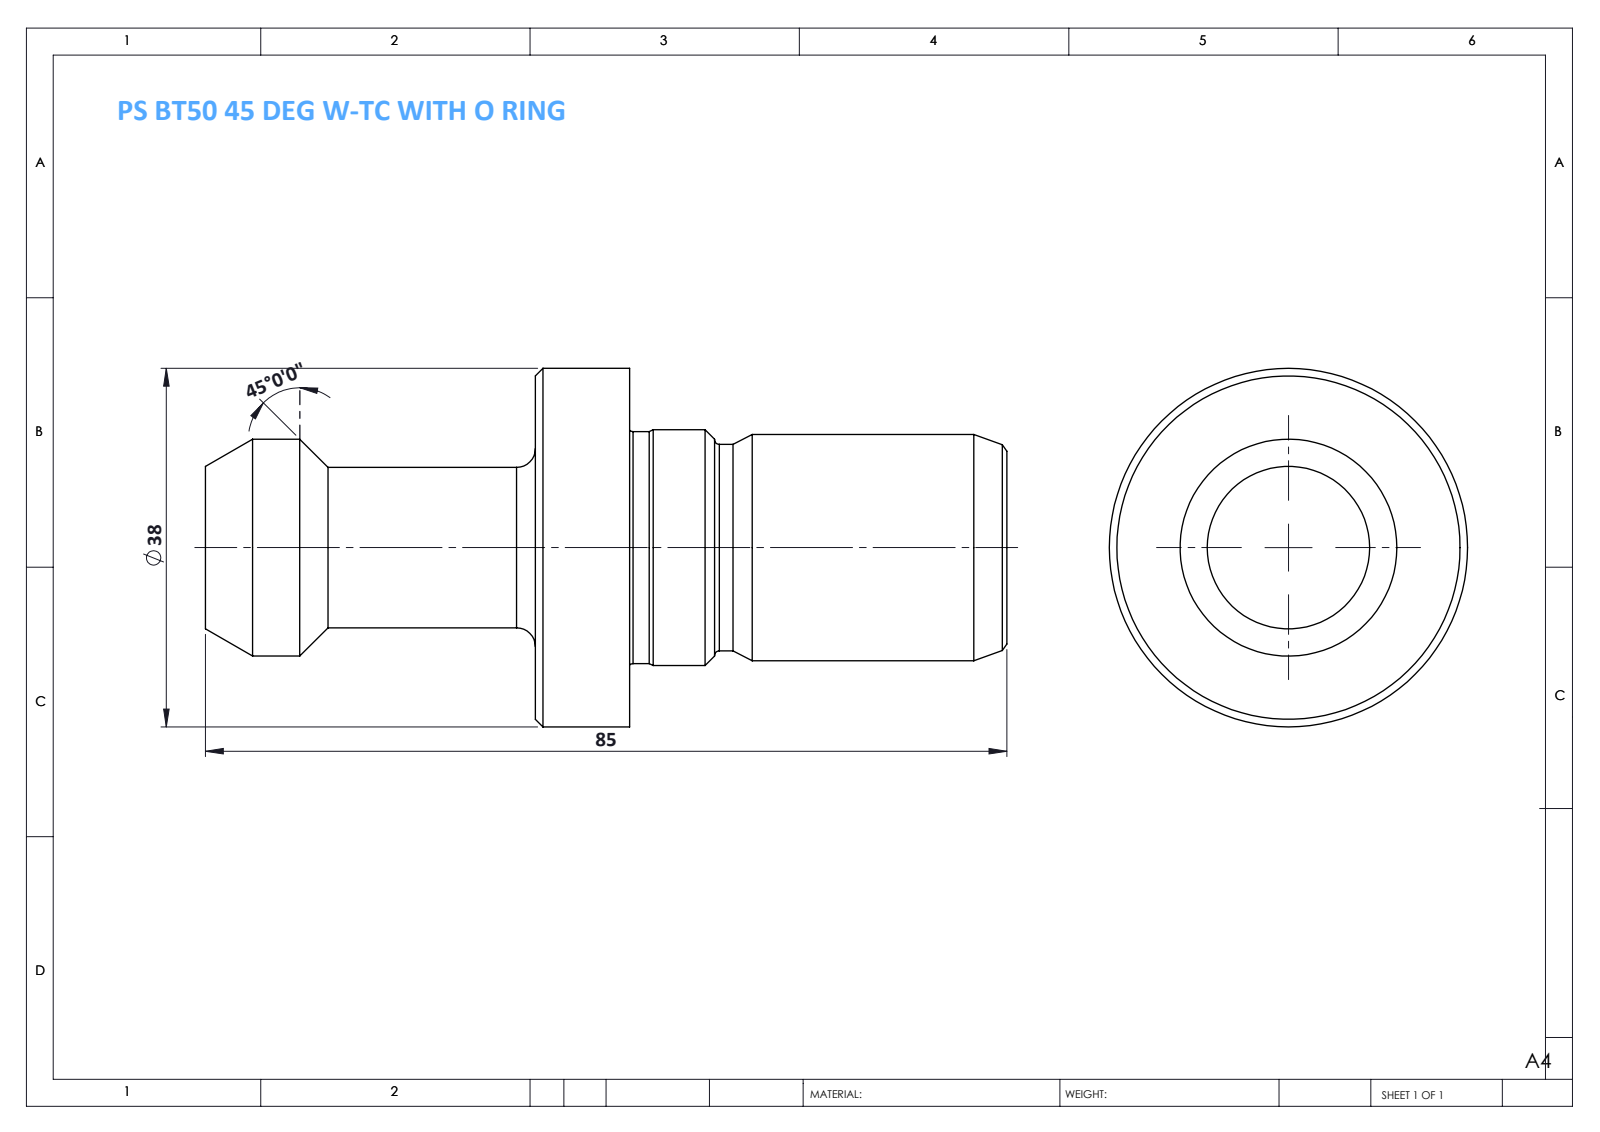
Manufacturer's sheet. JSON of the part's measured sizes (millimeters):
{"part_name": "PS BT50 45 DEG W-TC WITH O RING", "step_written_by": "SolidWorks 2014 (CONFIG_CONTROL_DESIGN)", "units": "millimeters", "bodies": {"solids": 1, "faces": 43, "planar": 5, "cylindrical": 14, "other": 24}, "overall_size": [85, 38, 38], "volume_mm3": 38941, "surface_area_mm2": 8503, "round_bosses_or_shafts": [[38, 1], [25, 1], [24.6, 1], [24, 1], [23, 1], [21.9, 1], [17, 1]], "face_to_face_distances": [10, 40, 50, 85, 45, 35, 31, 9, 19, 54]}
